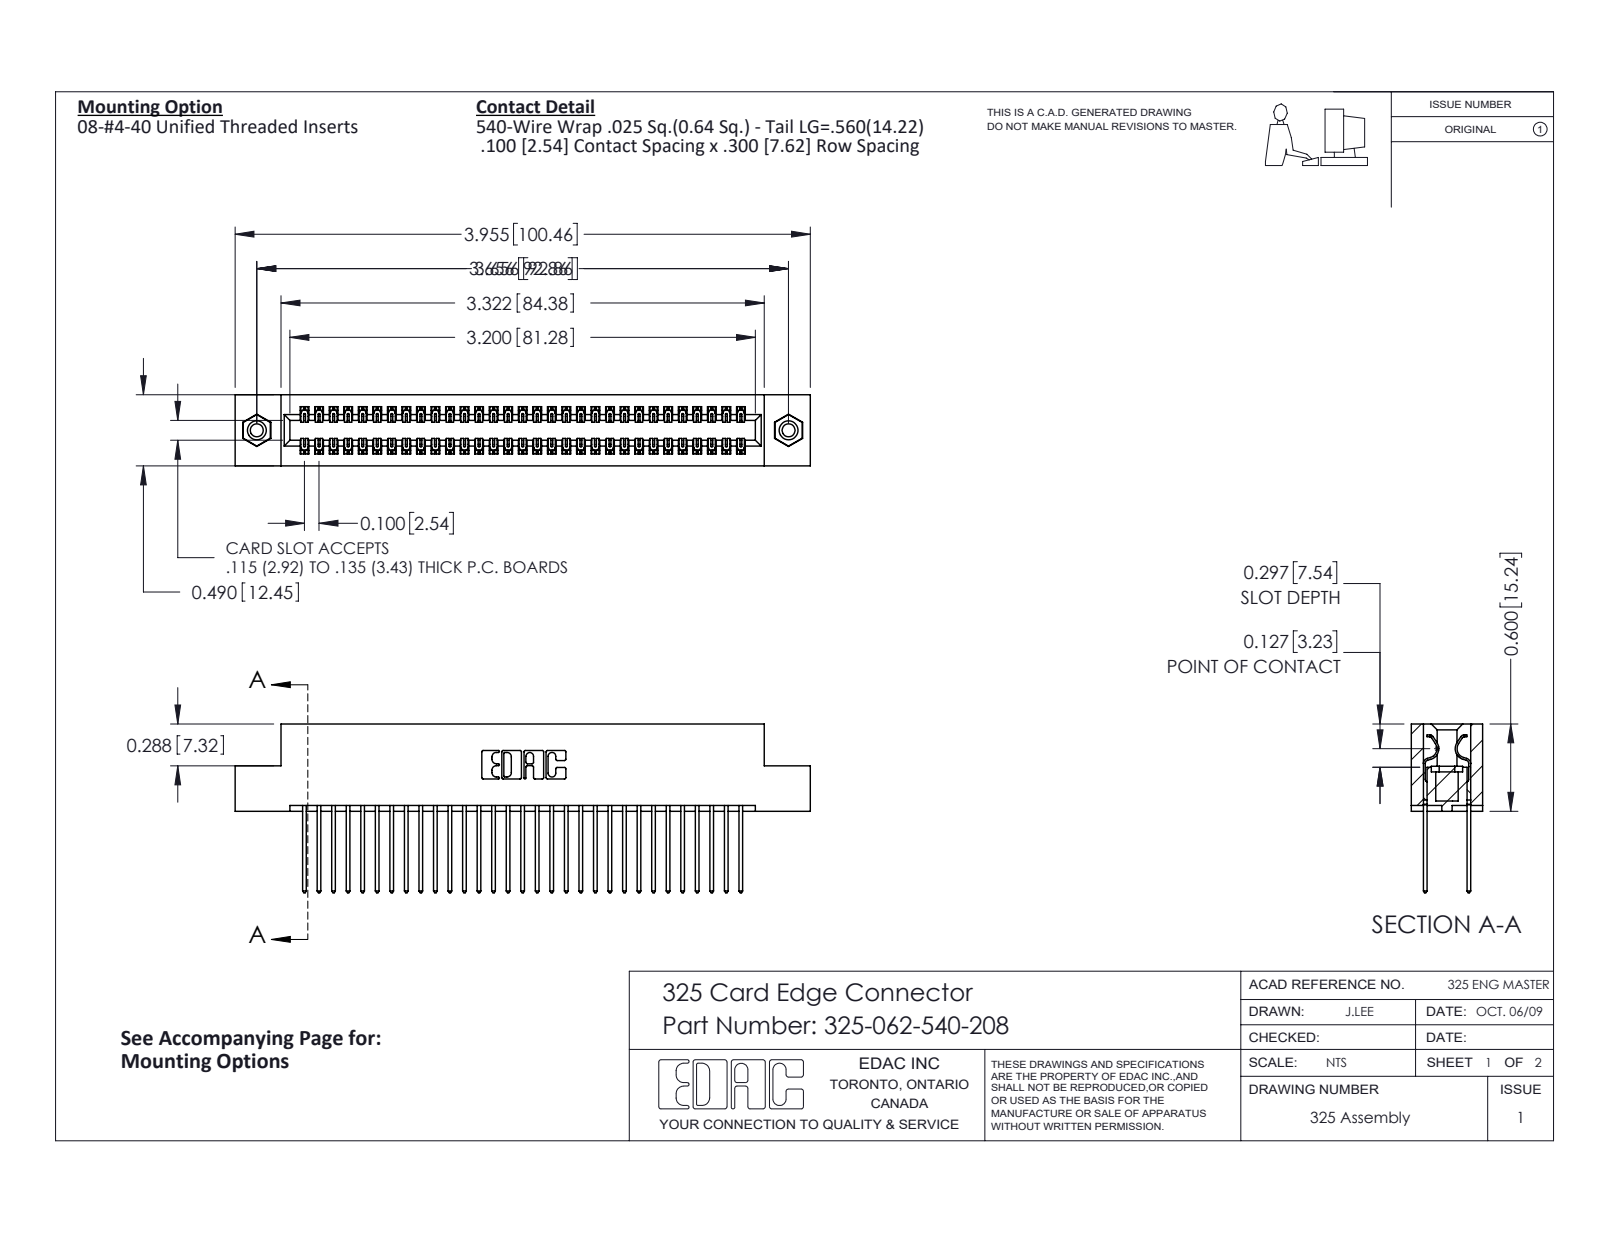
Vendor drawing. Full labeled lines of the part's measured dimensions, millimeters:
Part name (STEP PRODUCT): 325-292-001_325-293-140; 325-062-540-208; 345-250-001_345-250-003-102; 325 Part_TI
STEP written by: SolidWorks 2016 (CONFIG_CONTROL_DESIGN)
Units: millimetres
Bodies: 65 solids, 3398 faces (2334 planar, 1048 cylindrical, 16 other)
Overall size (bounding box): 100.5 × 29.5 × 12.4
Volume: 13 100 mm³ · Surface area: 16 720 mm²
Round holes (diameter × count): ⌀2.3 ×2, ⌀3.2 ×2, ⌀4.1 ×2
Round bosses / shafts (diameter × count): ⌀3.9 ×2
Partial cylindrical surfaces — rounded edges, fillets, slot ends (radius × count): R0.2 ×93, R0.3 ×62, R0.3 ×22, R0.2 ×6, R0.8 ×6, R0.7 ×3, R0.4 ×2, R0.6 ×2
Main face-to-face distances: 2.1, 10.3, 7.6, 2.7, 9.7, 0.6, 12.4, 8.3, 7, 1
Hole centre spacings: 92.9
